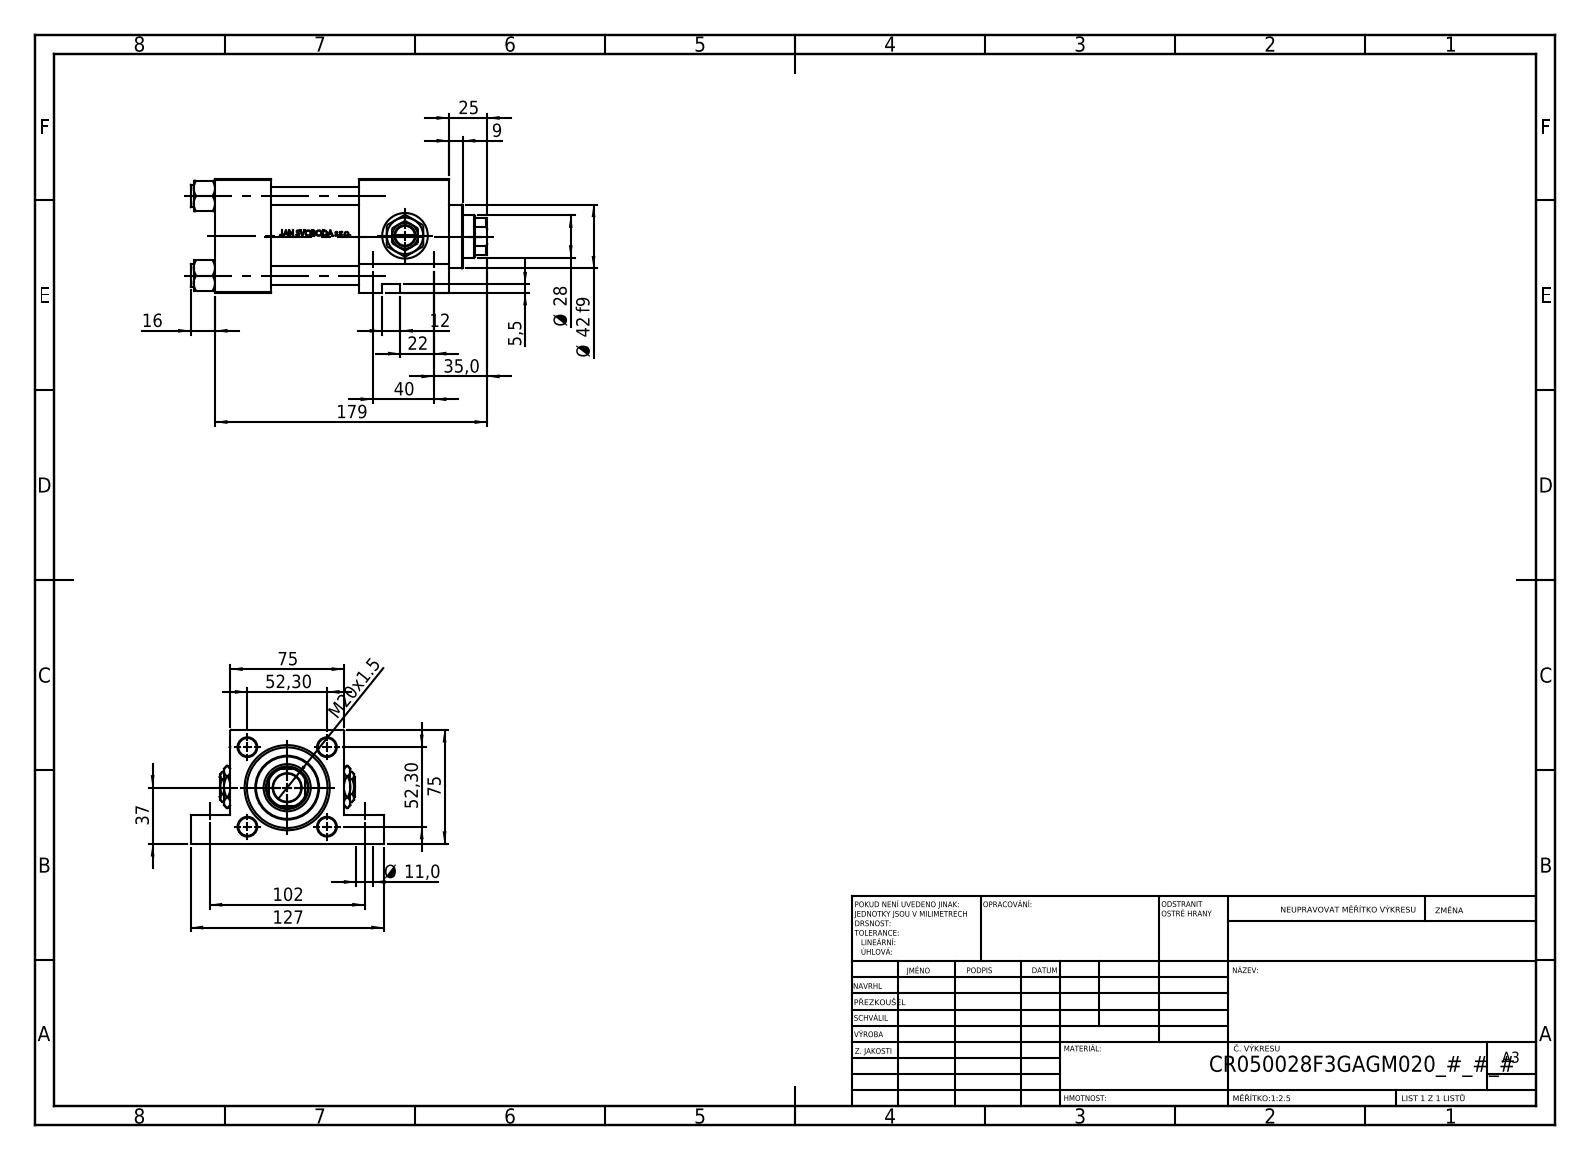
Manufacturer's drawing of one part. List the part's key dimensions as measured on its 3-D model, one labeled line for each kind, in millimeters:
Part name (STEP PRODUCT): V215CR_VCP_F; Zatka_pro_OIL_PORT; V215CR_F_Body; NUT_M5_F (+2 more)
STEP written by: SolidWorks 2019 (CONFIG_CONTROL_DESIGN)
Units: millimetres
Bodies: 13 solids, 1197 faces (483 planar, 132 cylindrical, 582 other)
Overall size (bounding box): 195 × 127 × 75
Volume: 720 521 mm³ · Surface area: 163 737 mm²
Round holes (diameter × count): ⌀12 ×4, ⌀7 ×3, ⌀30 ×3, ⌀11 ×2, ⌀11 ×2, ⌀20.96 ×2, ⌀17 ×1, ⌀18.5 ×1, ⌀28 ×1, ⌀31 ×1, ⌀41 ×1, ⌀50 ×1
Round bosses / shafts (diameter × count): ⌀15 ×4, ⌀56 ×1, ⌀42 ×1
Partial cylindrical surfaces — rounded edges, fillets, slot ends (radius × count): R13.5 ×1
Main face-to-face distances: 75, 37, 154, 117, 58, 95, 59, 19, 56, 125.3
Hole centre spacings: 52.3, 36.63, 37.34, 40, 73.96, 99.56, 102, 109.56
